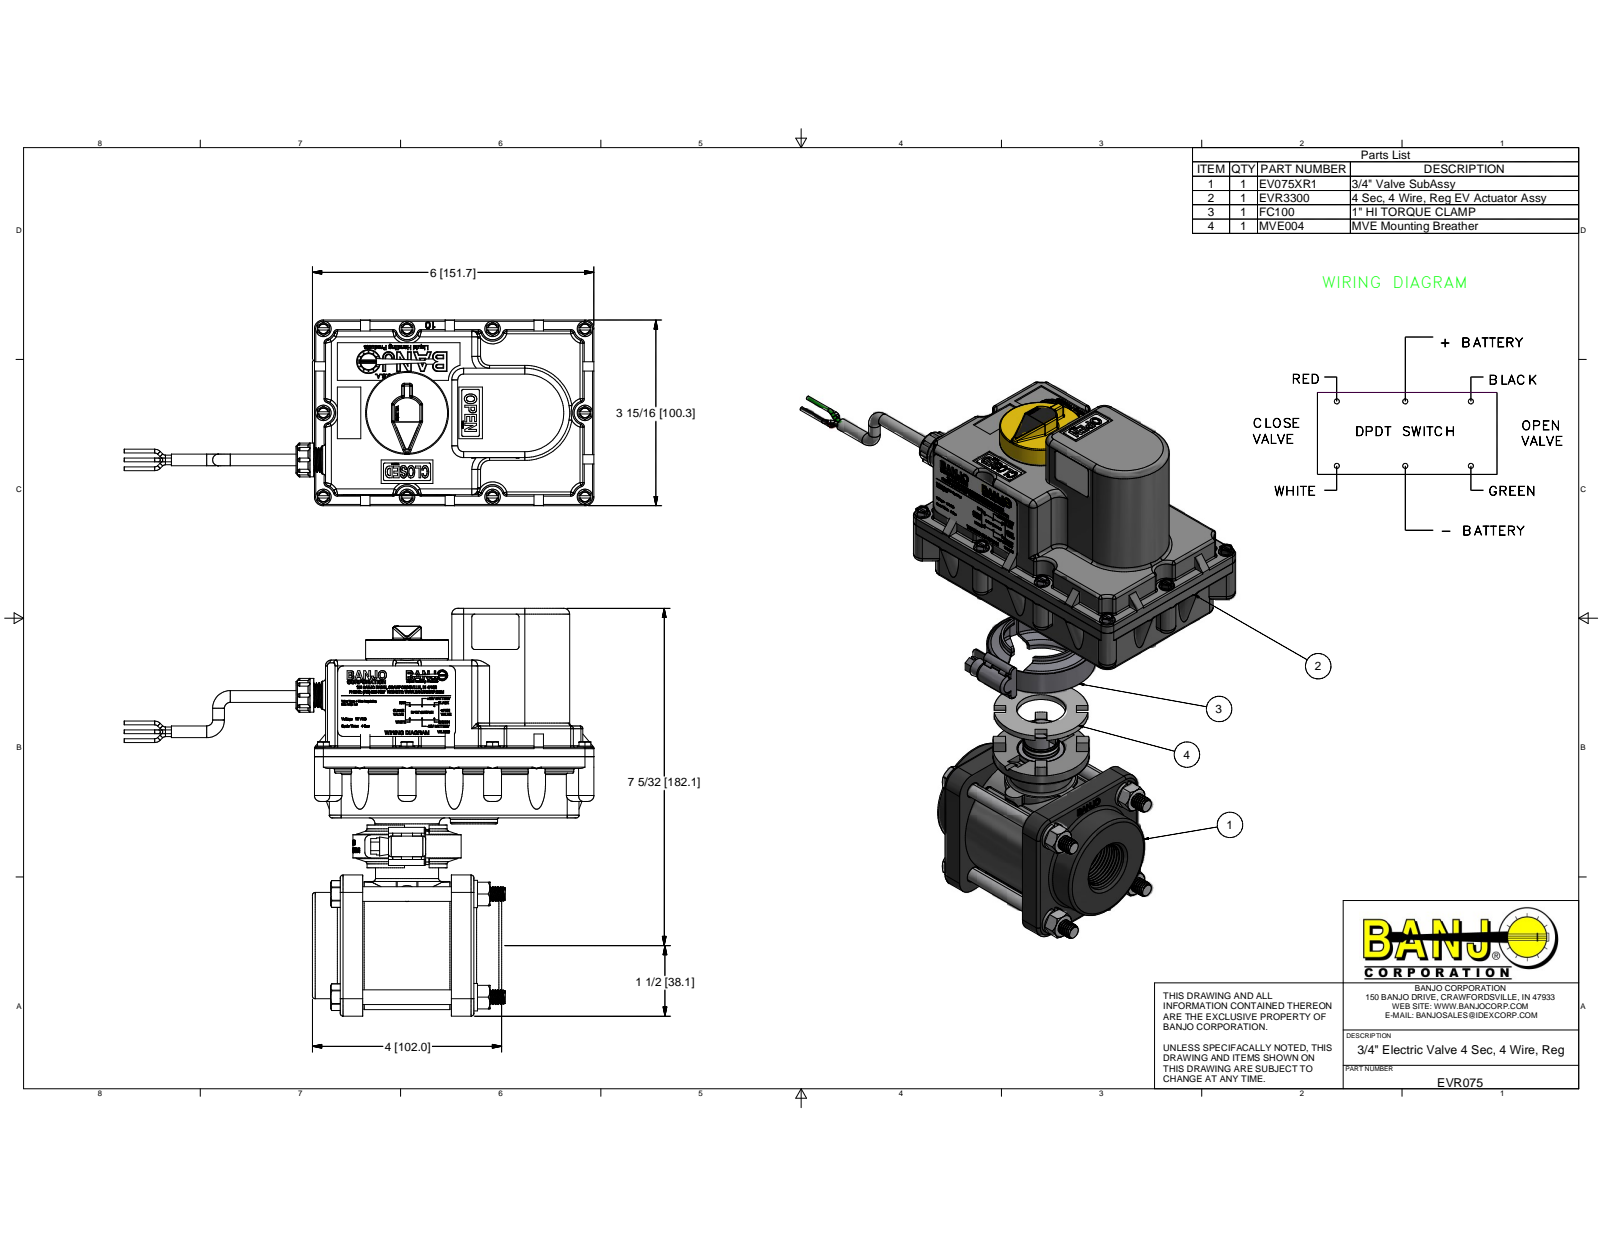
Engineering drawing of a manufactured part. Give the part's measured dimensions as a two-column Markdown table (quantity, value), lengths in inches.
| quantity | value |
| --- | --- |
| part name | MEV10254AX; MEV10254A; VE10155SSH; MEV10151SS (+8 more) |
| STEP written by | Autodesk Inventor 2016 (AUTOMOTIVE_DESIGN) |
| units | inches |
| bodies | 62 solids, 10018 faces (4699 planar, 1662 cylindrical, 3657 other) |
| overall size | 9.965 × 8.668 × 3.95 |
| volume | 55.15 in³ |
| surface area | 588.6 in² |
| round holes (diameter × count) | 0.16 × 11, 0.11 × 10, 0.2 × 10, 0.015 × 6, 0.12 × 6, 0.15 × 6, 0.176 × 6, 0.252 × 4, 0.322 × 4, 0.35 × 4, 1.02 × 3, 0.1 × 2 |
| round bosses / shafts (diameter × count) | 0.269 × 60, 0.08 × 19, 0.328 × 10, 0.138 × 10, 0.103 × 8, 0.025 × 6, 0.583 × 4, 0.316 × 4 |
| partial cylindrical surfaces (radius × count) | 0.03 × 143, 0.06 × 79, 0.02 × 63, 0.125 × 32, 0.315 × 24, 0.5 × 24, 0.39 × 16, 0.25 × 14 |
| main face-to-face distances | 0.125, 0.125, 0.2, 1.1, 0.78, 1.3, 0.475, 0.79, 3.23, 2.565 |
| hole center spacings | 1.68, 2.058, 1.684, 1.785, 2.376, 0.492, 1.188, 1.265 |
